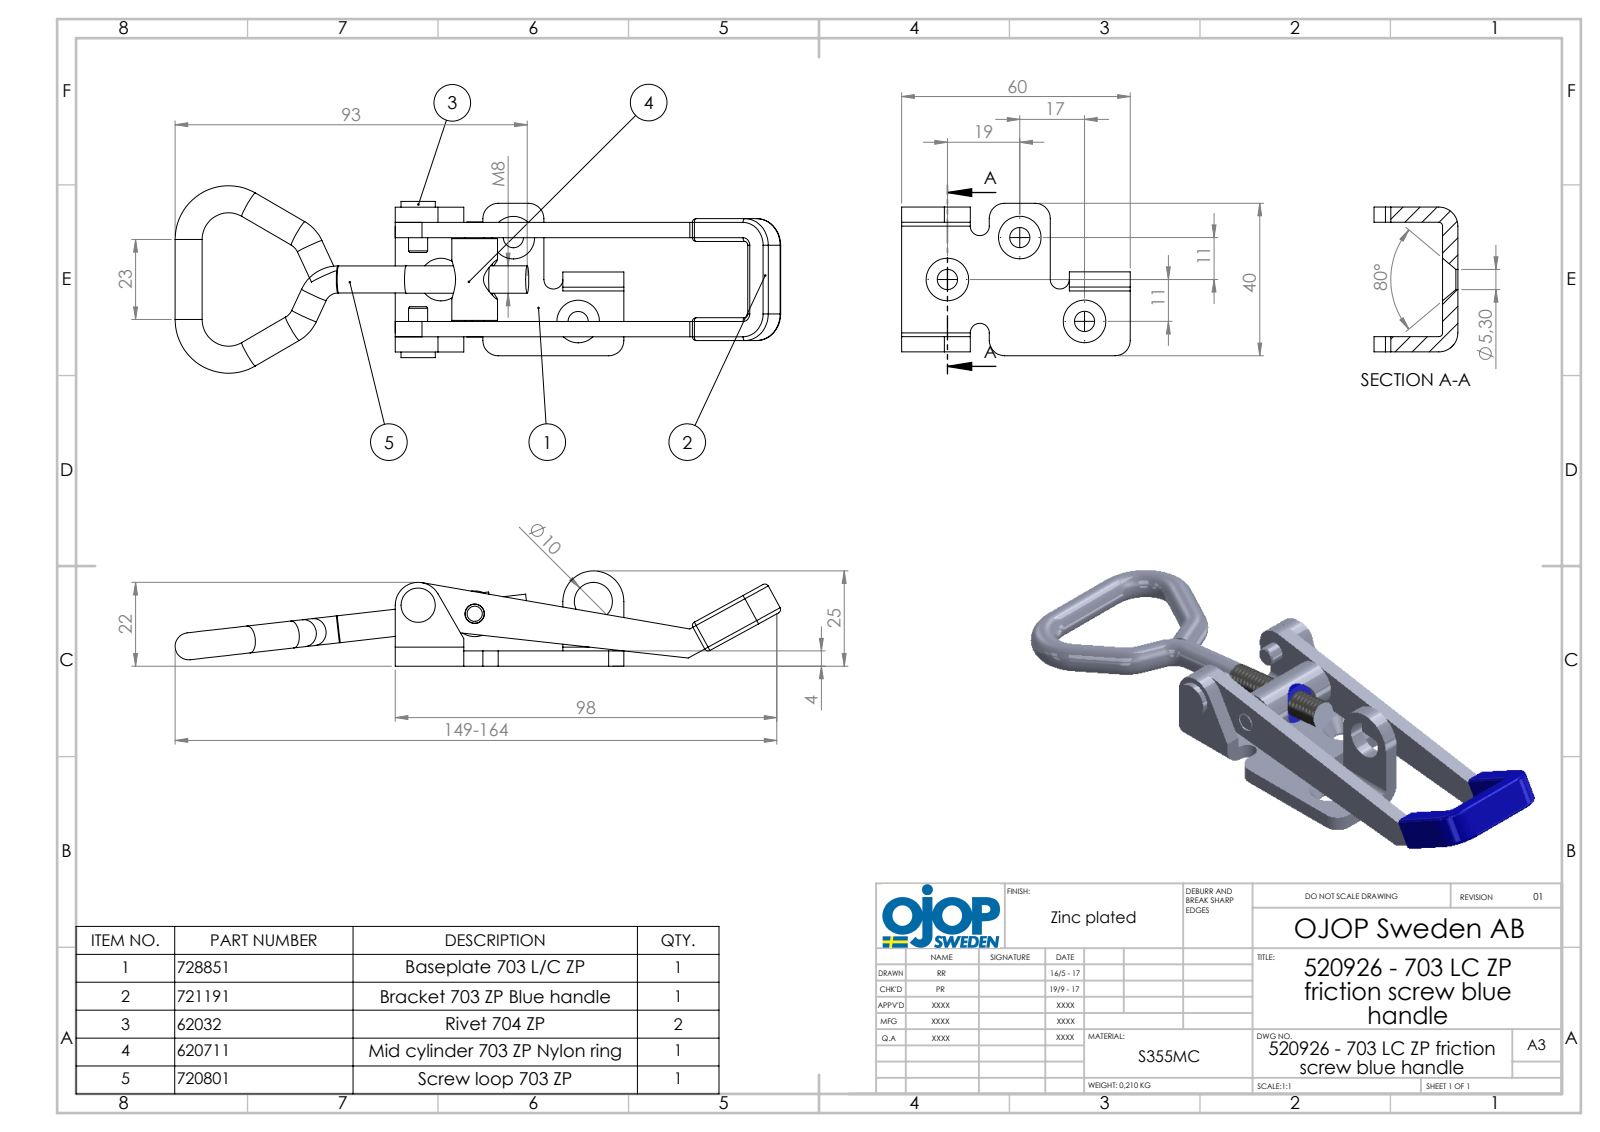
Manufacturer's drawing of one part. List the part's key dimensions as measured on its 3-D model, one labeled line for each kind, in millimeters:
Part name (STEP PRODUCT): 520926; 703 - Skruvögla; 704 - Mid Cylinder Friction ring; 704 - Mid Cylinder Friction (+4 more)
STEP written by: SolidWorks 2015 (AUTOMOTIVE_DESIGN)
Units: millimetres
Bodies: 7 solids, 221 faces (71 planar, 100 cylindrical, 50 other)
Overall size (bounding box): 165.68 × 49.4 × 25
Volume: 28 606 mm³ · Surface area: 19 140 mm²
Round holes (diameter × count): ⌀5.3 ×3, ⌀5.1 ×2, ⌀6.9 ×1, ⌀7.2 ×1, ⌀7.7 ×1, ⌀10 ×1, ⌀10.5 ×1
Round bosses / shafts (diameter × count): ⌀7 ×4, ⌀5 ×2, ⌀12 ×1, ⌀10.5 ×1, ⌀9 ×1, ⌀7.7 ×1
Partial cylindrical surfaces — rounded edges, fillets, slot ends (radius × count): R1 ×21, R4 ×4, R2.5 ×3, R5 ×3, R0.75 ×2, R7.25 ×2, R6 ×1, R8 ×1
Main face-to-face distances: 4, 26.7, 30.7, 17, 22.7, 13, 21, 9, 1.25, 5.25
Hole centre spacings: 15.02, 21.95, 27.8, 31.34, 37.64, 46.01
